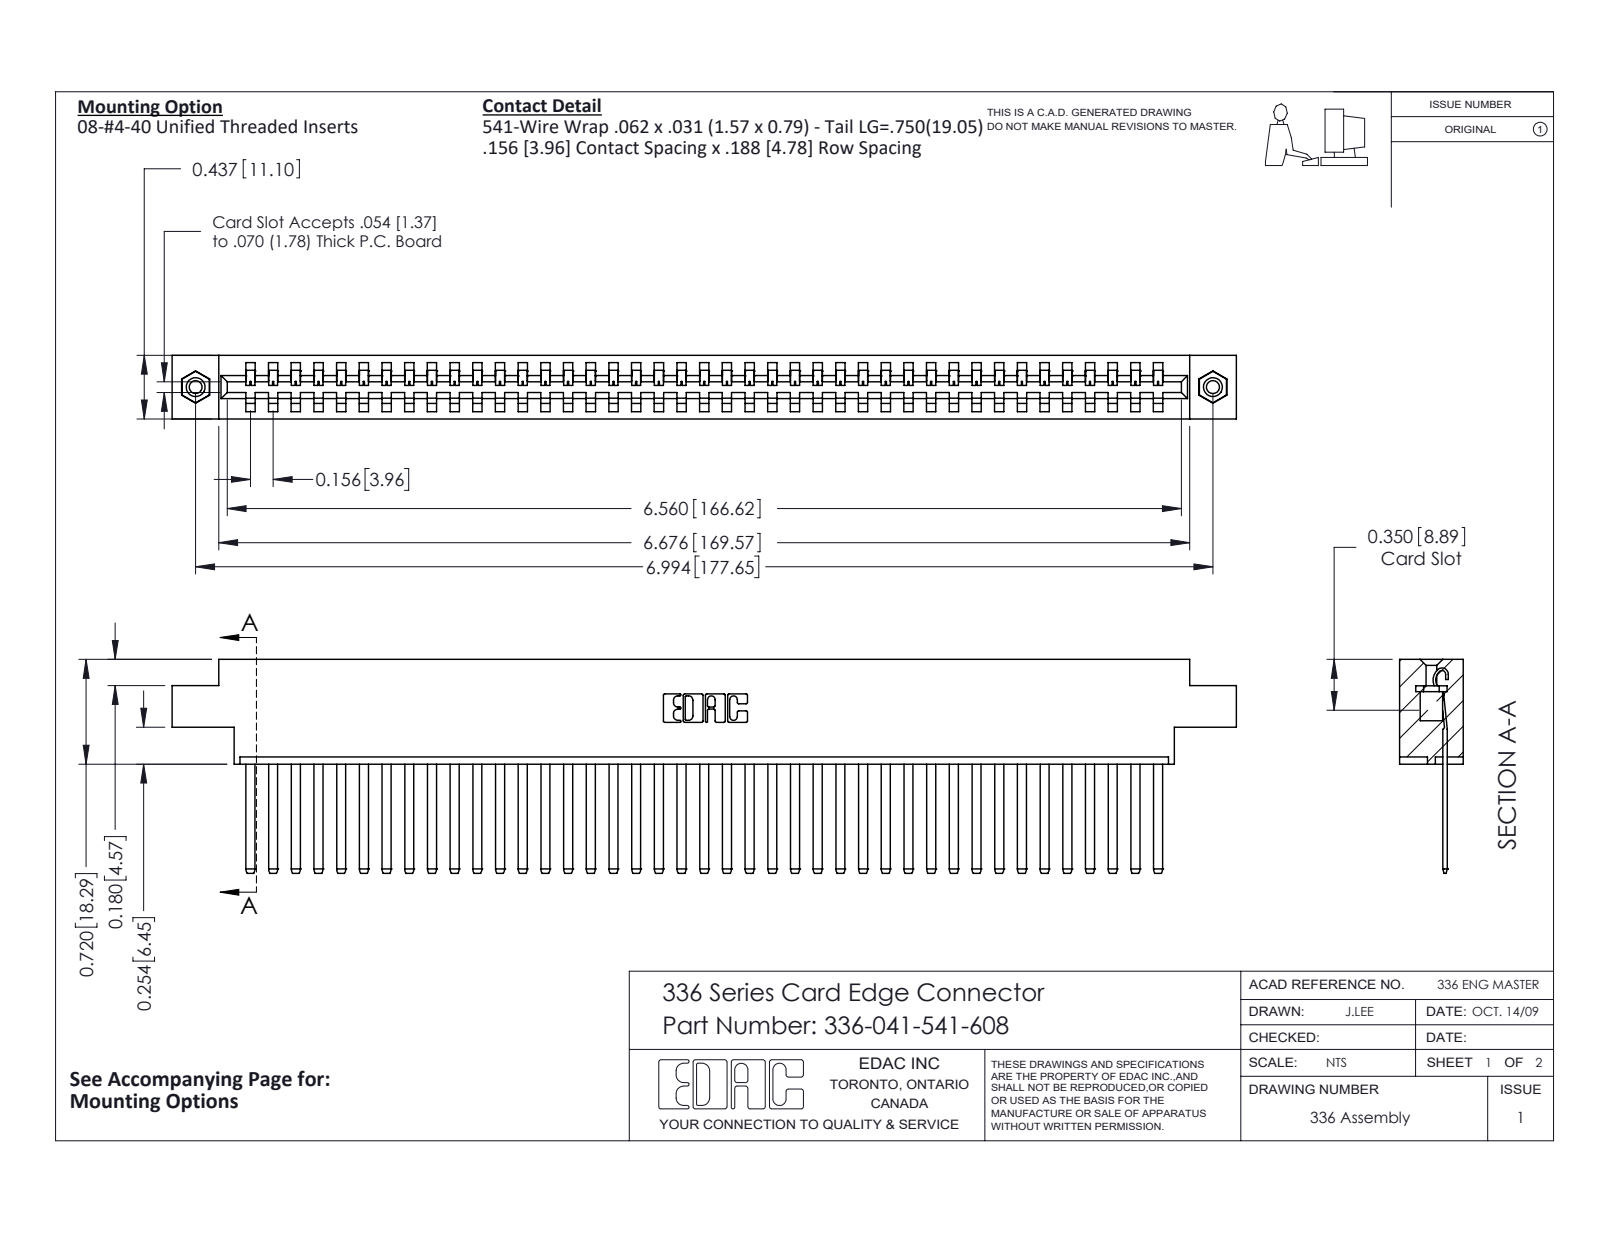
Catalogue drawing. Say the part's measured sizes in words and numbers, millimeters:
The part is named "336 Part_Offset - .156 Dia - TI; 336-290-001_336-290-541; 345-250-001_345-250-003-102; 336-041-541-608". Its 3-D file was written by "SolidWorks 2020 (CONFIG_CONTROL_DESIGN)". It is 44 solids with 2228 faces: 1500 planar, 712 cylindrical and 16 other. Overall it measures 185.9 by 37.3 by 11.1 millimeters. Its volume is 27 040 cubic millimeters and its surface area 29 540 square millimeters. Round holes: 2 of diameter 2.3, 2 of diameter 3.2, 2 of diameter 4. Round bosses or shafts: 2 of diameter 3.9. Partial cylindrical surfaces (rounded edges, fillets, slot ends): 82 of radius 0.1, 82 of radius 1.4, 22 of radius 0.3, 6 of radius 0.2, 6 of radius 0.8, 3 of radius 0.7, 2 of radius 0.6, 2 of radius 1. The main face-to-face distances are 11.1, 4.6, 8.3, 3.6, 7.5, 2.8, 0.8, 6.5, 1.3, 3.3. The hole center spacings are 177.6.
